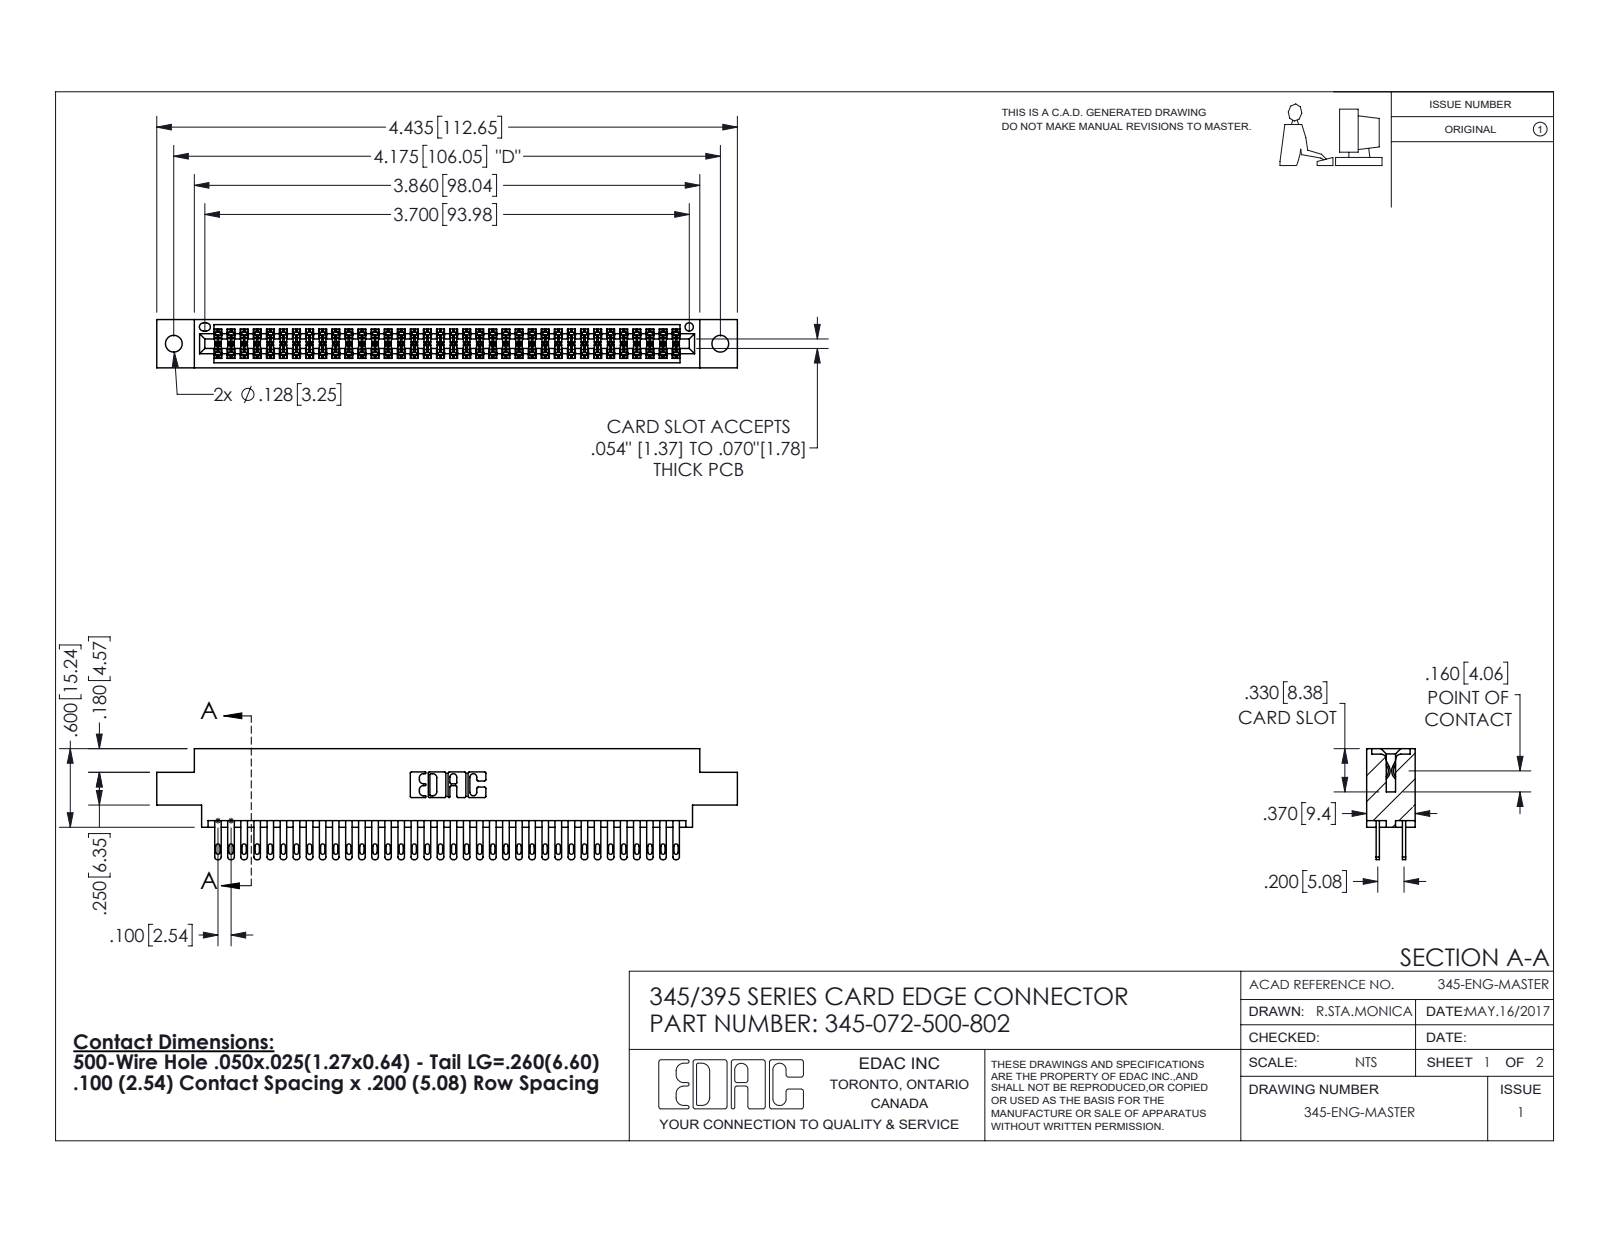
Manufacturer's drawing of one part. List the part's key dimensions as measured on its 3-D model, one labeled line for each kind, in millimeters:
Part name (STEP PRODUCT): 345-072-500-802; 345-292-001_345-293-100; 345 Part_0.170 Offset - 0.128 Dia
STEP written by: SolidWorks 2016 (CONFIG_CONTROL_DESIGN)
Units: millimetres
Bodies: 73 solids, 3442 faces (2028 planar, 1414 cylindrical, 0 other)
Overall size (bounding box): 112.6 × 21.5 × 9.4
Volume: 11 000 mm³ · Surface area: 16 680 mm²
Round holes (diameter × count): ⌀3.3 ×2, ⌀1.6 ×1
Partial cylindrical surfaces — rounded edges, fillets, slot ends (radius × count): R0.2 ×108, R0.4 ×72, R0.5 ×72, R0.3 ×22, R0.2 ×6, R0.8 ×6, R0.7 ×3, R0.4 ×2
Main face-to-face distances: 7.6, 1.8, 5.1, 2.5, 6.9, 0.6, 9.4, 5.7, 4.4, 3.8
Hole centre spacings: 6.9, 100.1, 106
